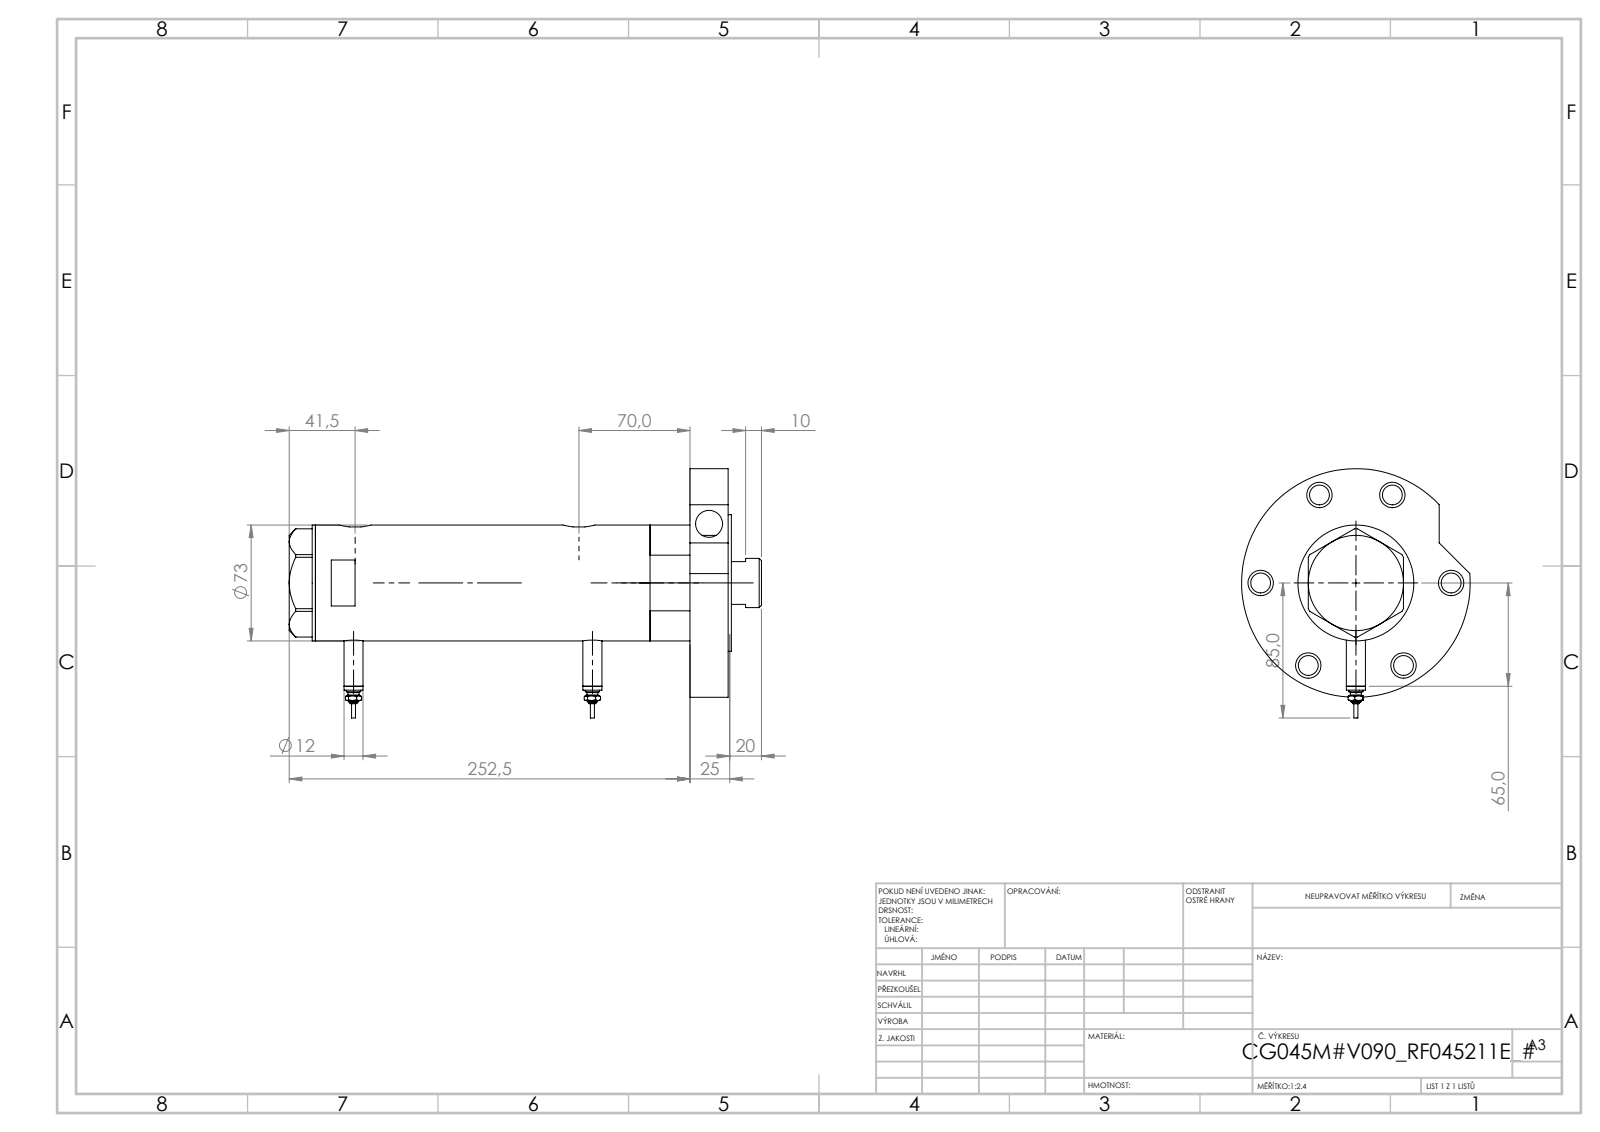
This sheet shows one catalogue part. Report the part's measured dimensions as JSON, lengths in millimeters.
{"part_name": "V270CG_MIDDLE; Switch; V270CG_RF211E; V270CG_BACK (+2 more)", "step_written_by": "SolidWorks 2019 (CONFIG_CONTROL_DESIGN)", "units": "millimeters", "bodies": {"solids": 7, "faces": 256, "planar": 88, "cylindrical": 104, "other": 64}, "overall_size": [297.5, 157, 144], "volume_mm3": 1323000, "surface_area_mm2": 225650, "round_holes": [[12.5, 8], [16, 6], [13.16, 2], [10.5, 1], [17, 1], [32, 1], [33.5, 1], [45, 1], [48, 1], [60, 1], [64, 1]], "round_bosses_or_shafts": [[12, 2], [9, 2], [7, 2], [4.5, 2], [2.5, 2], [144, 1], [86, 1], [73, 1]], "partial_cylinders_radius": [[10, 2]], "face_to_face_distances": [24, 236, 26, 2, 260, 262, 1, 166, 70, 94], "hole_center_spacings": [60, 66.67, 99.77, 103.92, 107.62, 119.74, 1, 8.5]}
